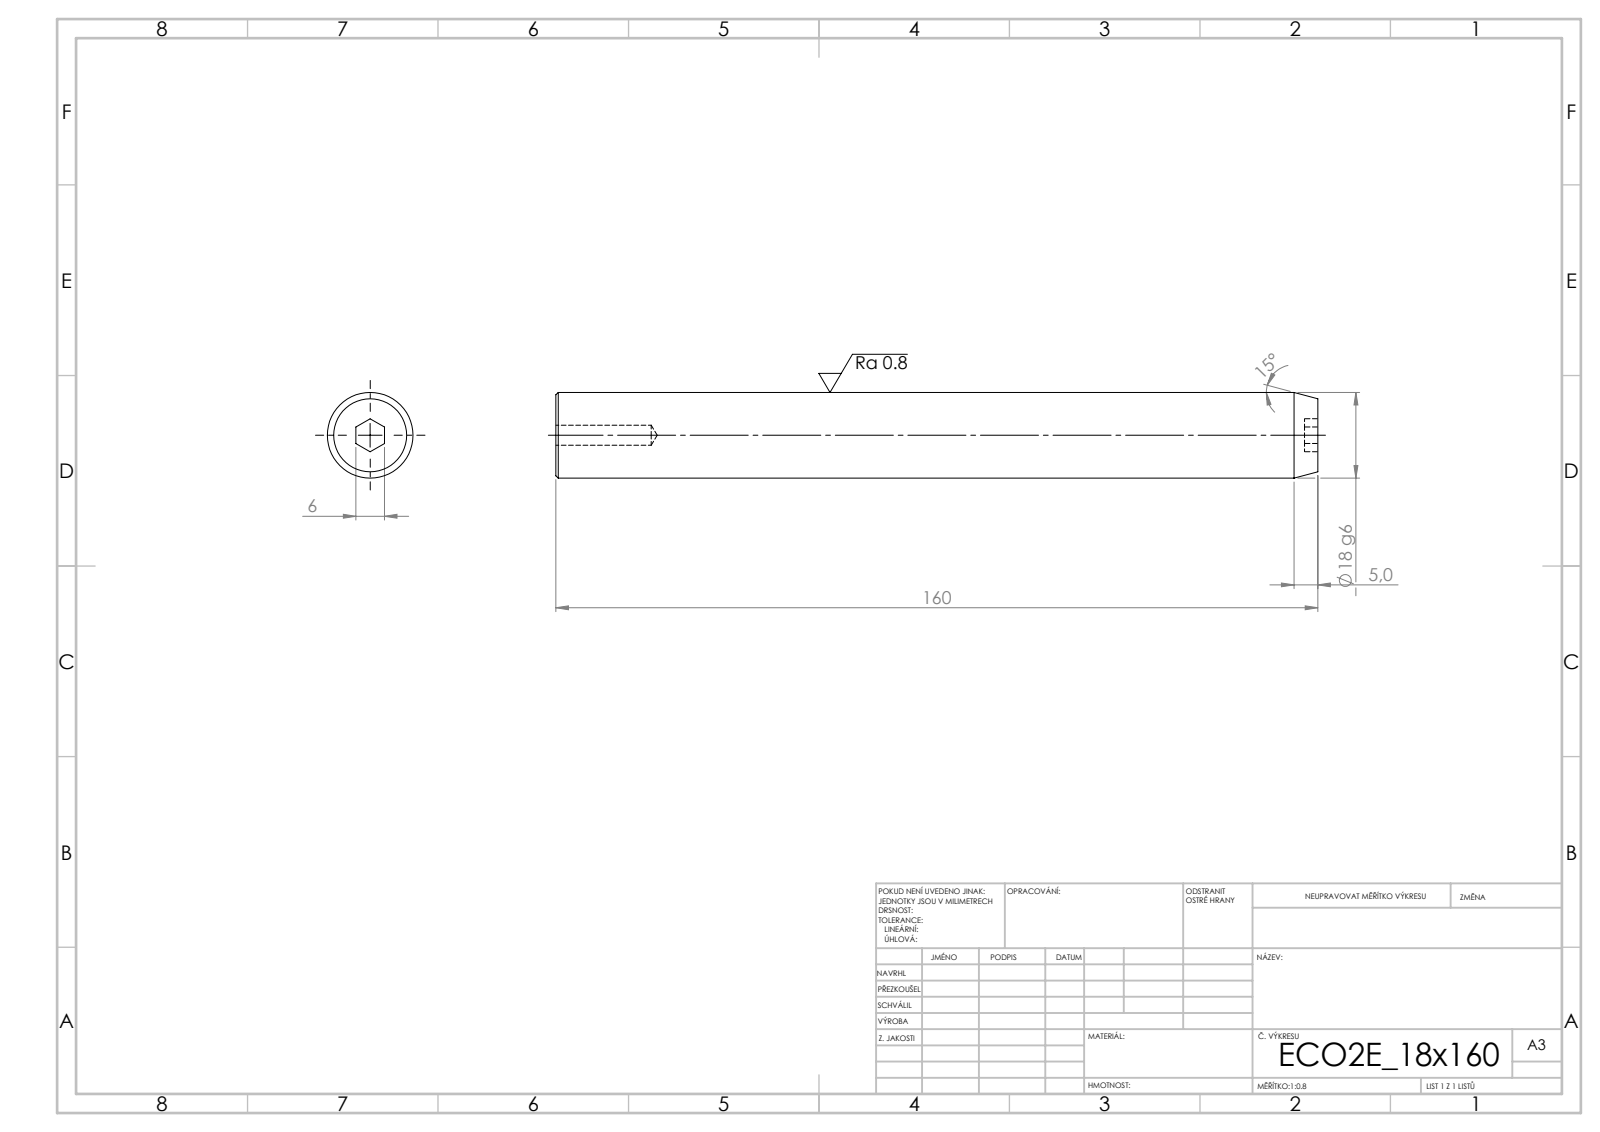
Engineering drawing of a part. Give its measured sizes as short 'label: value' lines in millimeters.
written by: SolidWorks 2019 (CONFIG_CONTROL_DESIGN)
unit: mm
bodies: 1 solid, 19 faces (9 planar, 4 cylindrical, 6 other)
size: 160 × 18 × 18
volume: 40 158 mm³; area: 9 782 mm²
holes: 1× ⌀4.2
bosses: 1× ⌀18
face distances: 160, 2.8, 157.2, 6
